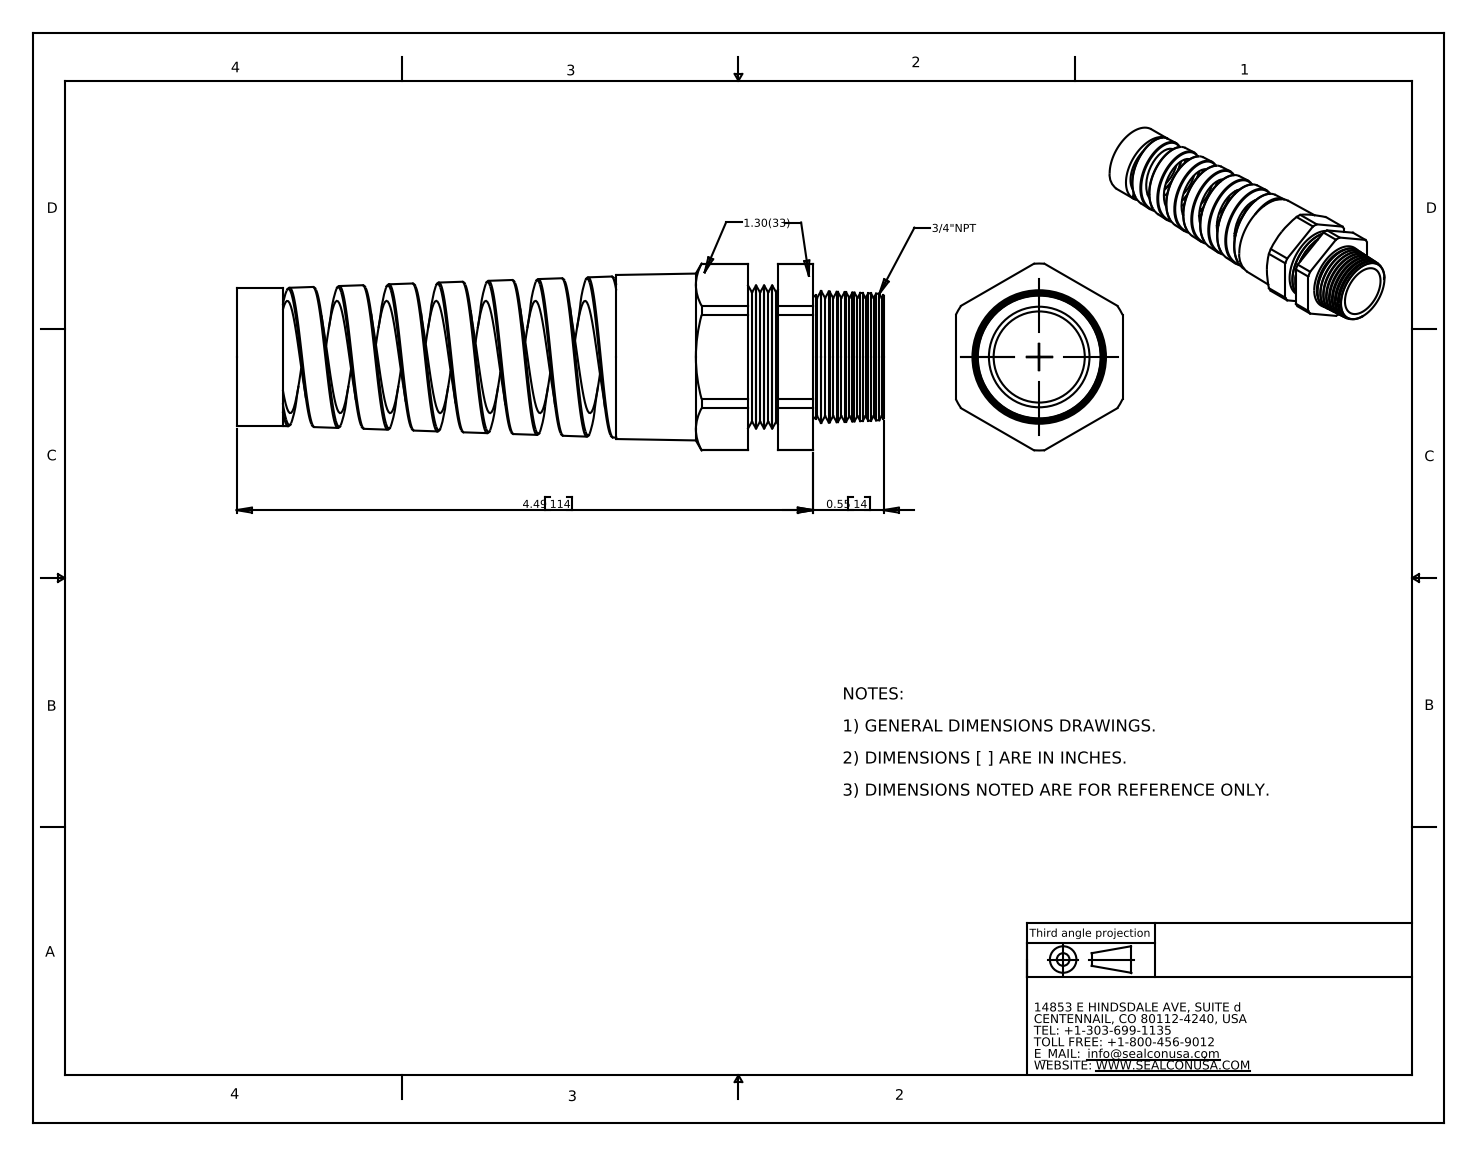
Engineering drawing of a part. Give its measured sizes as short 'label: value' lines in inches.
name: CF21NA-BK
written by: SolidWorks 2007 (CONFIG_CONTROL_DESIGN)
unit: in
bodies: 1 solid, 163 faces (19 planar, 39 cylindrical, 105 other)
size: 5.04 × 1.456 × 1.3
volume: 2.298 in³; area: 35.49 in²
holes: 1× ⌀0.71, 1× ⌀0.875
bosses: 1× ⌀1.113, 1× ⌀1.075
rounds: 1× R0.728
face distances: 1.3, 1.532, 1.026, 0.506, 1.259, 0.232, 0.274, 2.958, 3.984, 4.217
